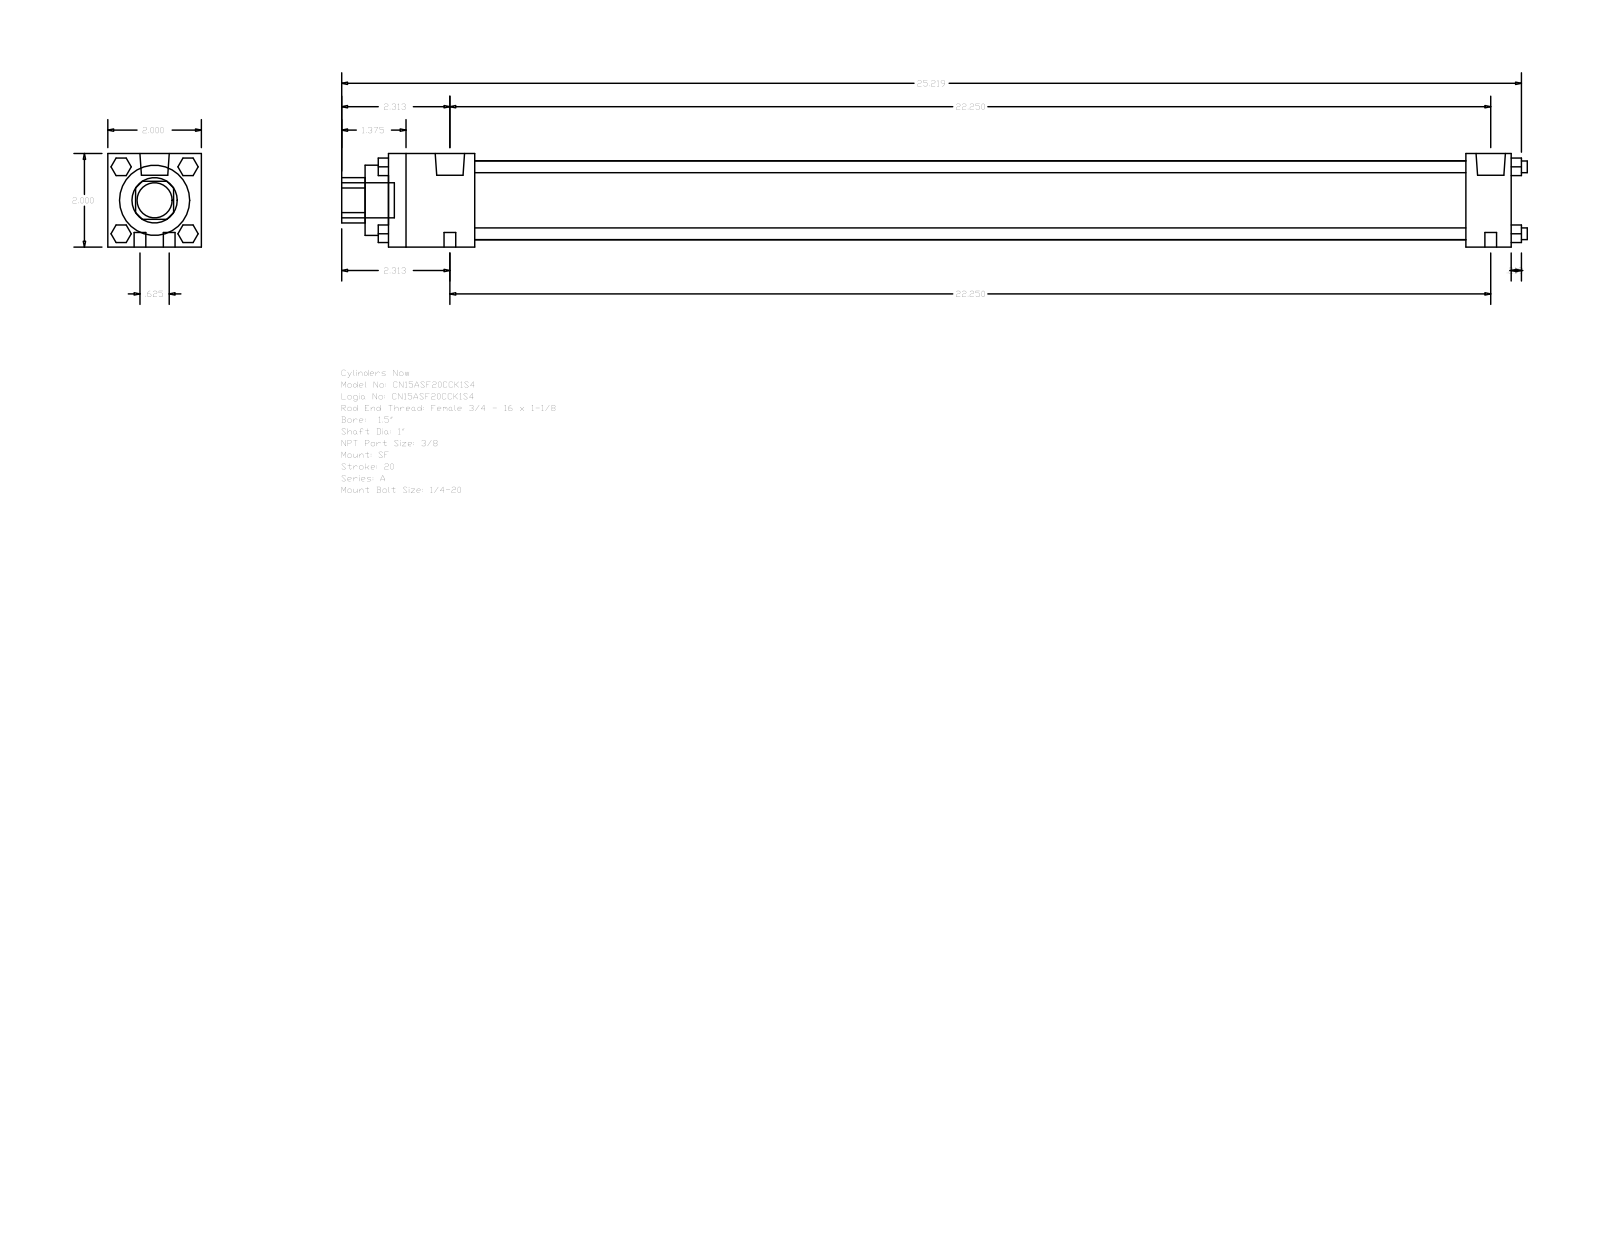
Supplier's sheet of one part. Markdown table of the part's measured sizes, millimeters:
| quantity | value |
| --- | --- |
| part name | A_SF__0150_1 |
| STEP written by | GSSL Pune (CONFIG_CONTROL_DESIGN) |
| units | millimeters |
| bodies | 0 solids, 124 faces (94 planar, 30 cylindrical, 0 other) |
| overall size | 643.73 × 50.8 × 50.8 |
| round holes (diameter × count) | 25.4 × 1, 38.1 × 1, 42.93 × 1 |
| round bosses / shafts (diameter × count) | 6.35 × 8, 15.93 × 2, 5.56 × 2, 19.05 × 1 |
| partial cylindrical surfaces (radius × count) | 12.29 × 1 |
| main face-to-face distances | 50.8, 609.6, 46.83, 584.99, 538.16, 562.77, 24.61, 12.7, 59.53, 597.69 |
